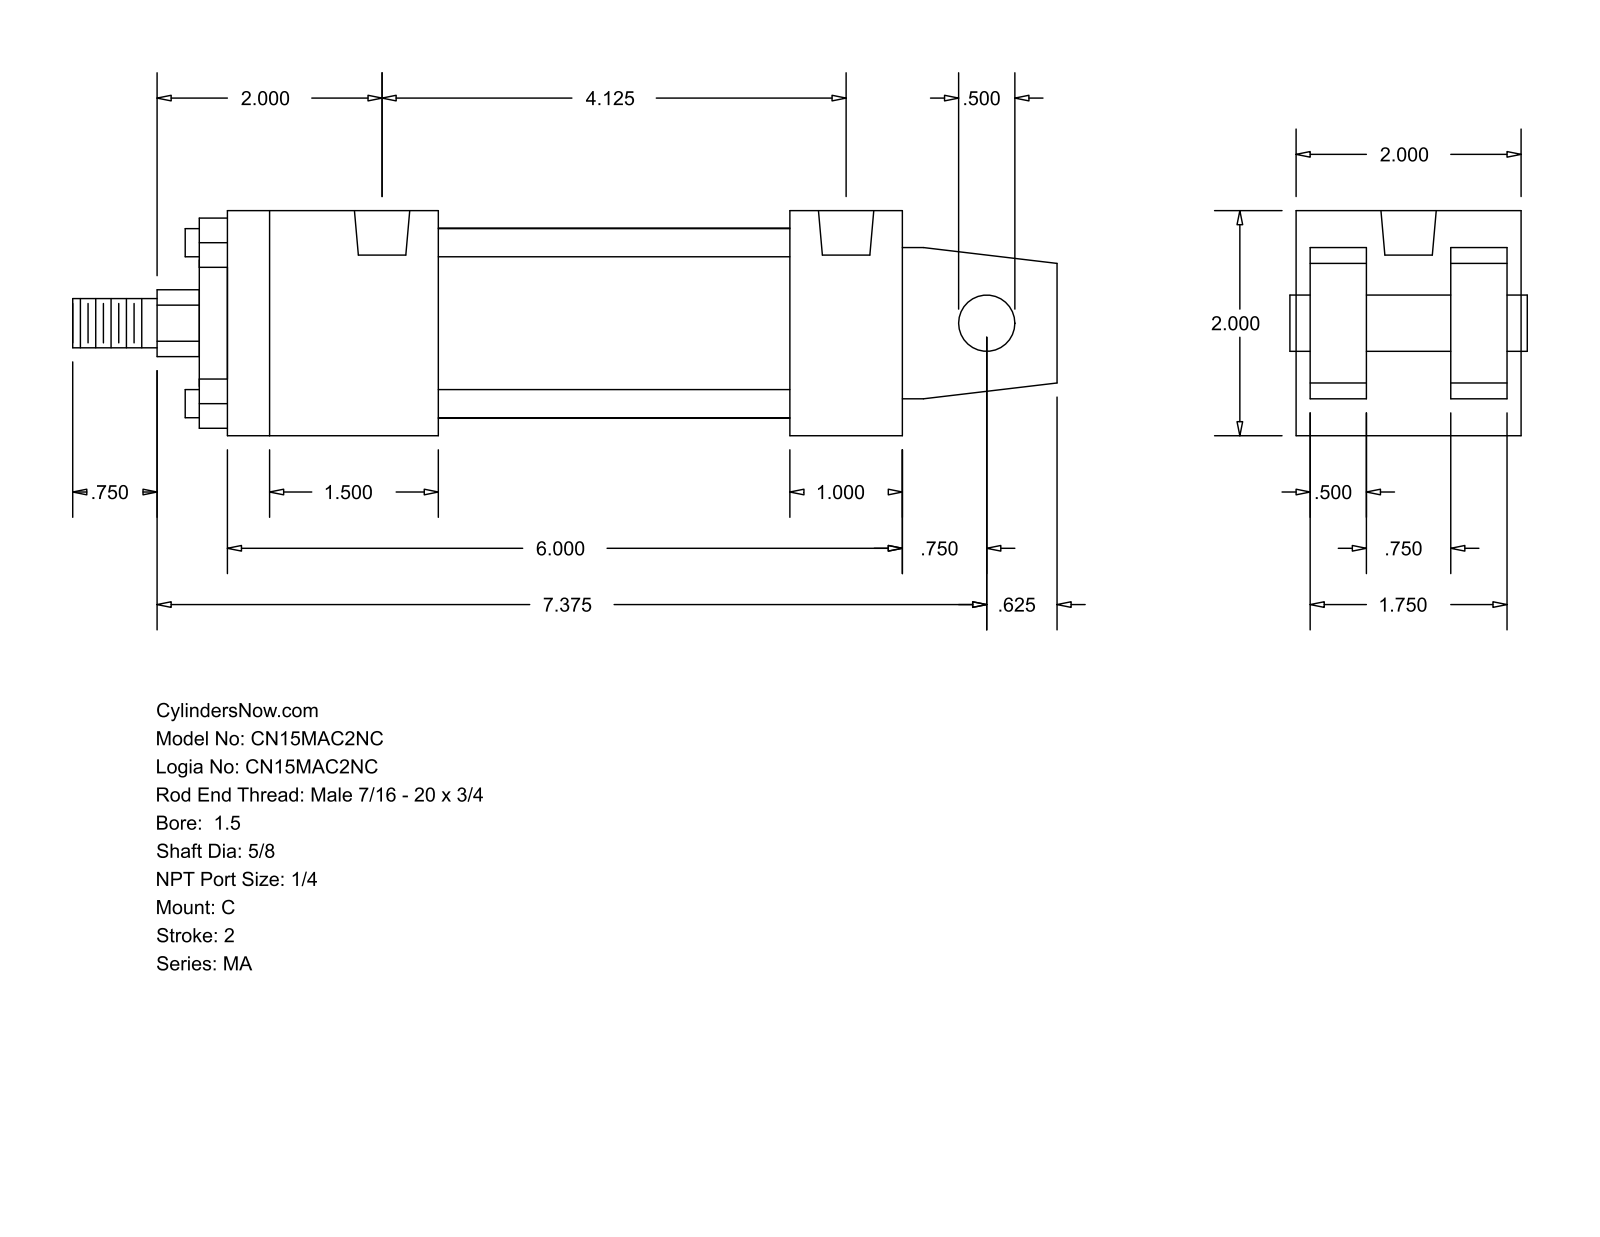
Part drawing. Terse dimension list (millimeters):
name: MA_C__0150_0.625
written by: GSSL Pune (CONFIG_CONTROL_DESIGN)
unit: mm
bodies: 0 solids, 103 faces (76 planar, 27 cylindrical, 0 other)
size: 222.25 × 50.8 × 50.8
holes: 4× ⌀7.94, 2× ⌀12.49
bosses: 4× ⌀6.35, 1× ⌀42.93, 1× ⌀28.57, 1× ⌀15.88, 1× ⌀12.7, 1× ⌀11.11
rounds: 1× R7.54
face distances: 50.8, 12.7, 34.93, 15.87, 3.17, 47.63, 31.76, 152.4, 25.4, 127
hole spacings: 104.77
